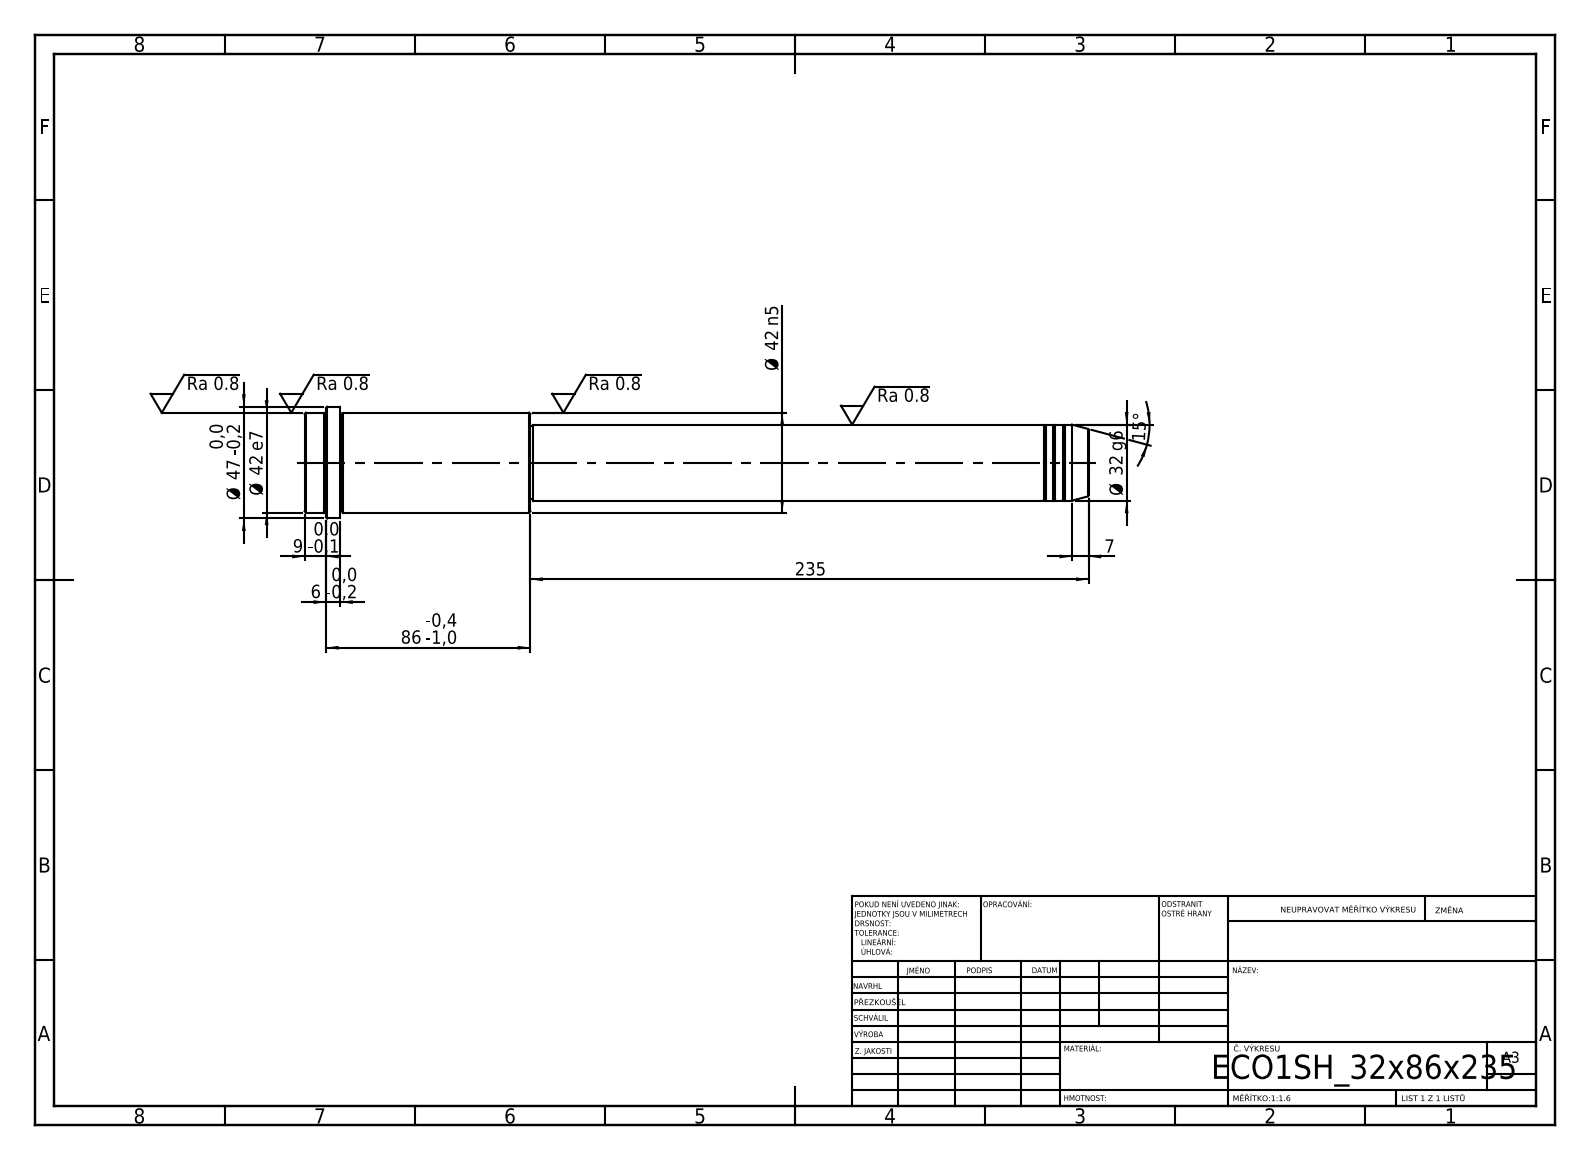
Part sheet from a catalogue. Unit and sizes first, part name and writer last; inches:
Units: inches
Overall size (bounding box): 12.992 × 1.85 × 1.85
Round bosses / shafts (diameter × count): ⌀1.85 ×1, ⌀1.654 ×1, ⌀1.26 ×1, ⌀1.22 ×1
Main face-to-face distances: 12.992, 9.252, 3.74, 12.402, 3.15, 0.591, 12.638, 3.386, 0.236, 0.354
Volume: 19.63 in³ · Surface area: 61.69 in²
Bodies: 1 solid, 52 faces (6 planar, 16 cylindrical, 30 other)
STEP written by: SolidWorks 2019 (CONFIG_CONTROL_DESIGN)
